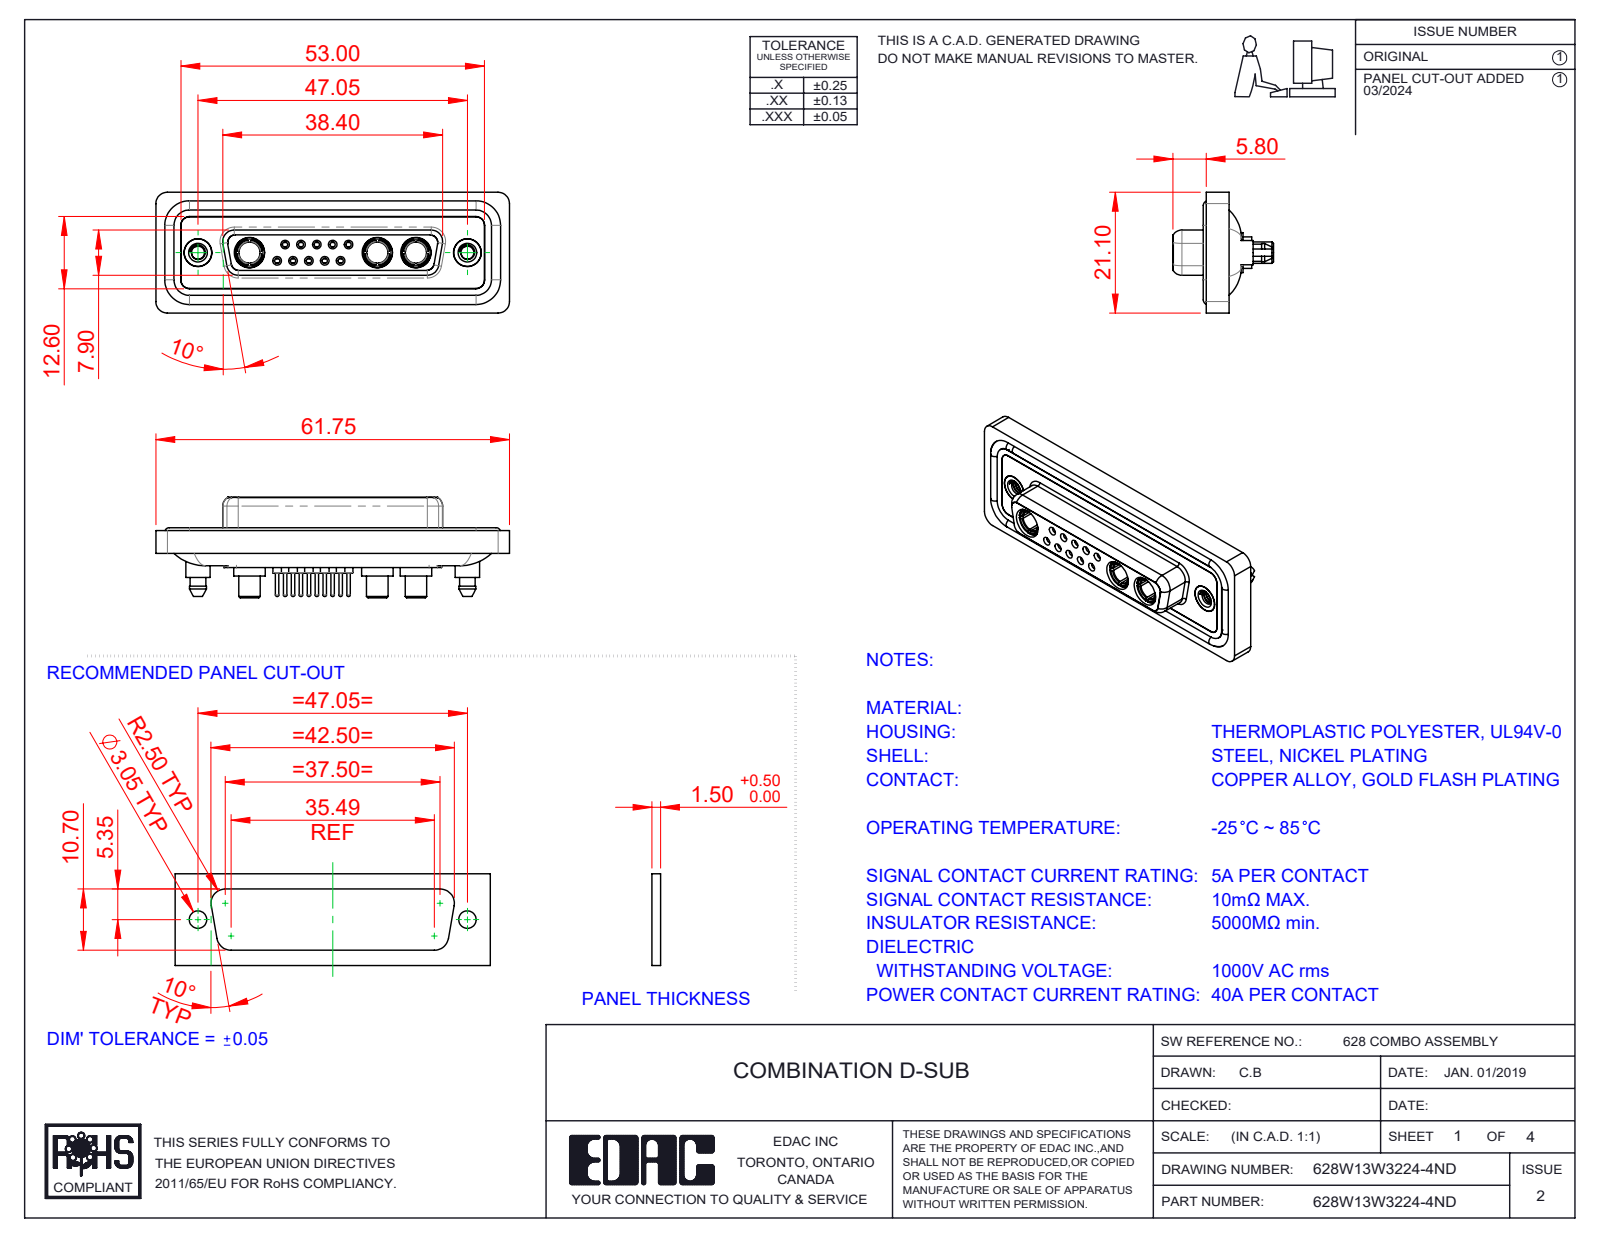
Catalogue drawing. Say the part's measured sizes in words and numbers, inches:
The part is named "628Combo Shell Front_25 Contacts; 628W13W3224-4ND; 628Combo Contact Row 2_24; Power Socket_40A S (+5 more)". Its 3-D file was written by "SolidWorks 2023 (CONFIG_CONTROL_DESIGN)". It is 23 solids with 1224 faces: 358 planar, 495 cylindrical and 371 other. Overall it measures 2.431 by 0.831 by 0.691 inches. Its volume is 0.517 cubic inches and its surface area 21.83 square inches. Round holes: 10 of diameter 0.035, 10 of diameter 0.043, 10 of diameter 0.059, 10 of diameter 0.079, 5 of diameter 0.063, 5 of diameter 0.067, 5 of diameter 0.191, 3 of diameter 0.146, 3 of diameter 0.209, 2 of diameter 0.089, 2 of diameter 0.157, 2 of diameter 0.159. Round bosses or shafts: 10 of diameter 0.087, 10 of diameter 0.024, 9 of diameter 0.063, 3 of diameter 0.217, 3 of diameter 0.205, 3 of diameter 0.195, 3 of diameter 0.187, 3 of diameter 0.148. Partial cylindrical surfaces (rounded edges, fillets, slot ends): 24 of radius 0.059, 18 of radius 0.079, 10 of radius 0.063, 8 of radius 0.053, 4 of radius 0.01, 4 of radius 0.02, 4 of radius 0.024, 4 of radius 0.026. The main face-to-face distances are 0.016, 0.071, 0.293, 0.222, 0.02, 0.26, 0.278, 0.063, 0.114, 0.043. The hole center spacings are 0.124, 0.109, 0.198, 0.198, 0.218, 0.327, 0.295, 0.109.
